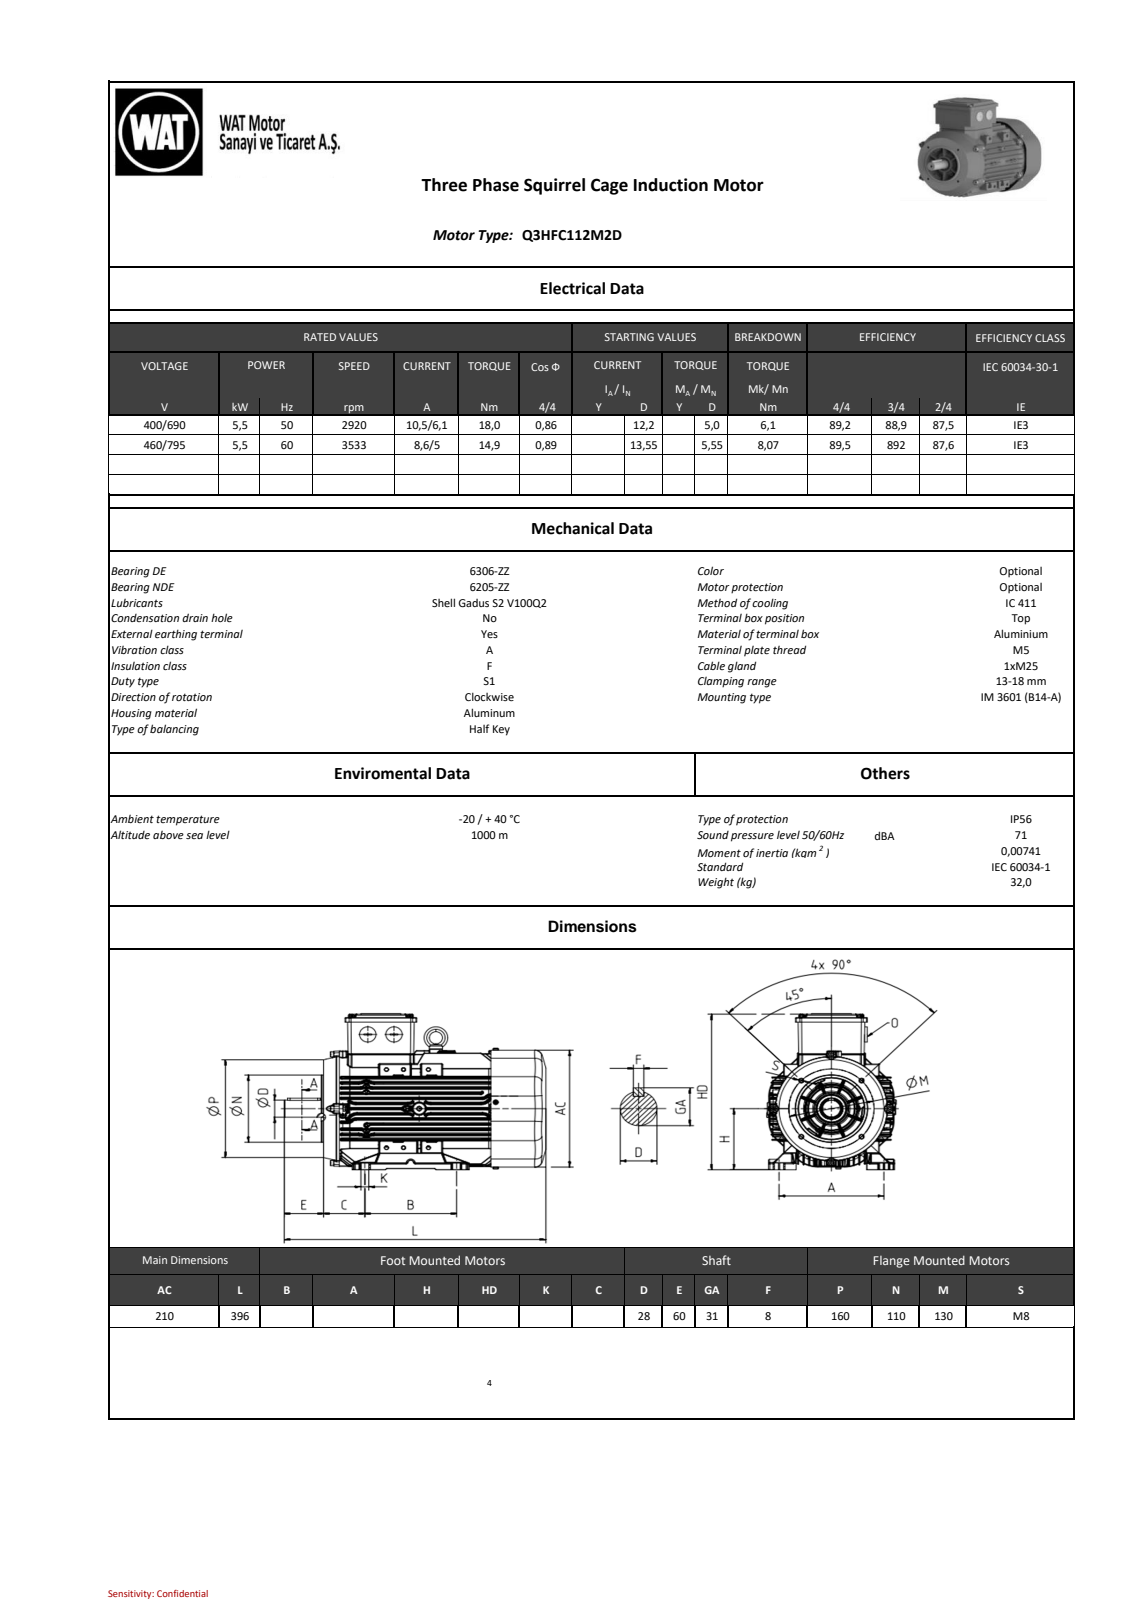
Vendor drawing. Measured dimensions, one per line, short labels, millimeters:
name: QH Series_ 112_B14a_stp_objects
written by: SIEMENS PLM Software NX2206.8101 (AUTOMOTIVE_DESIGN)
unit: mm
bodies: 0 solids, 6103 faces (1376 planar, 2341 cylindrical, 2386 other)
size: 396 × 267.5 × 219
holes: 2× ⌀4.6, 1× ⌀8, 1× ⌀8.5, 1× ⌀47
bosses: 4× ⌀10, 4× ⌀8, 2× ⌀25, 2× ⌀6, 1× ⌀188, 1× ⌀110, 1× ⌀35.83, 1× ⌀30
rounds: 499× R2, 498× R0.8, 400× R0.5, 143× R1, 96× R1.2, 60× R3, 10× R4, 8× R2.5
face distances: 1, 10.99, 21.5, 35.96, 99.54, 24.97, 90.43, 68.93, 8.16, 112.88
